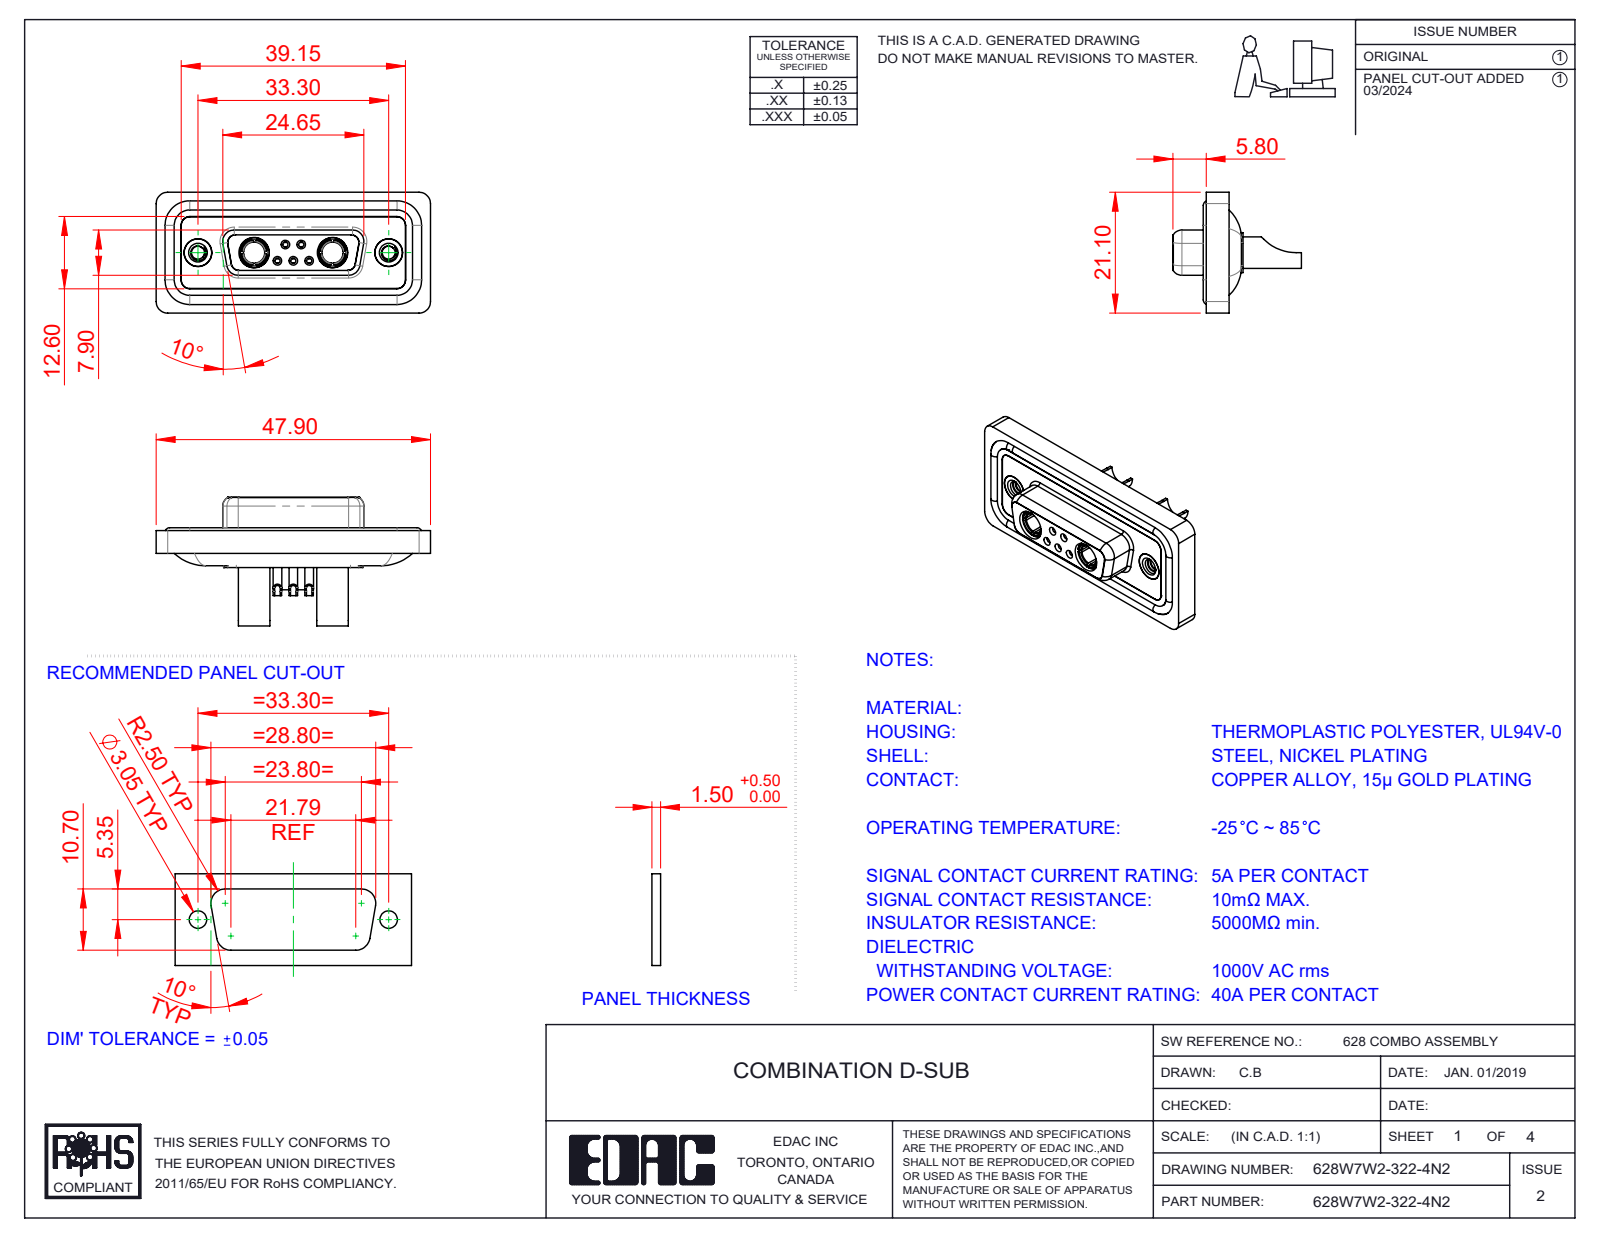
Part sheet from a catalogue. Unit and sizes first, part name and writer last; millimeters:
Units: millimetres
Overall size (bounding box): 47.9 × 22.45 × 21.1
Round holes (diameter × count): ⌀0.9 ×5, ⌀1 ×5, ⌀1.1 ×5, ⌀1.5 ×5, ⌀2 ×5, ⌀4.85 ×4, ⌀1.6 ×3, ⌀1.7 ×2, ⌀2.26 ×2, ⌀3.7 ×2, ⌀4 ×2, ⌀4.05 ×2
Round bosses / shafts (diameter × count): ⌀1.6 ×6, ⌀2.2 ×5, ⌀5.5 ×2, ⌀5.2 ×2, ⌀4.96 ×2, ⌀4.95 ×2, ⌀4.8 ×2, ⌀4.75 ×2
Partial cylindrical surfaces — rounded edges, fillets, slot ends (radius × count): R1.5 ×22, R2 ×20, R1.35 ×12, R1.6 ×8, R1 ×6, R0.25 ×4, R0.5 ×4, R0.6 ×4
Main face-to-face distances: 0.4, 1.6, 1.8, 0.5, 2.9, 1.1, 7.45, 5.65, 6.6, 7.05
Hole centre spacings: 3.16, 2.77, 9.8, 23.5, 4.31, 4.33, 5.03, 5.04
Volume: 6 168 mm³ · Surface area: 10 220 mm²
Bodies: 16 solids, 815 faces (252 planar, 341 cylindrical, 222 other)
Part name (STEP PRODUCT): 628Combo Contact Row 1_22; 628W7W2-322-4N2; 628Combo Waterproof Housing_15 Contacts; 628Combo Contact Row 2_22 (+5 more)
STEP written by: SolidWorks 2023 (CONFIG_CONTROL_DESIGN)
